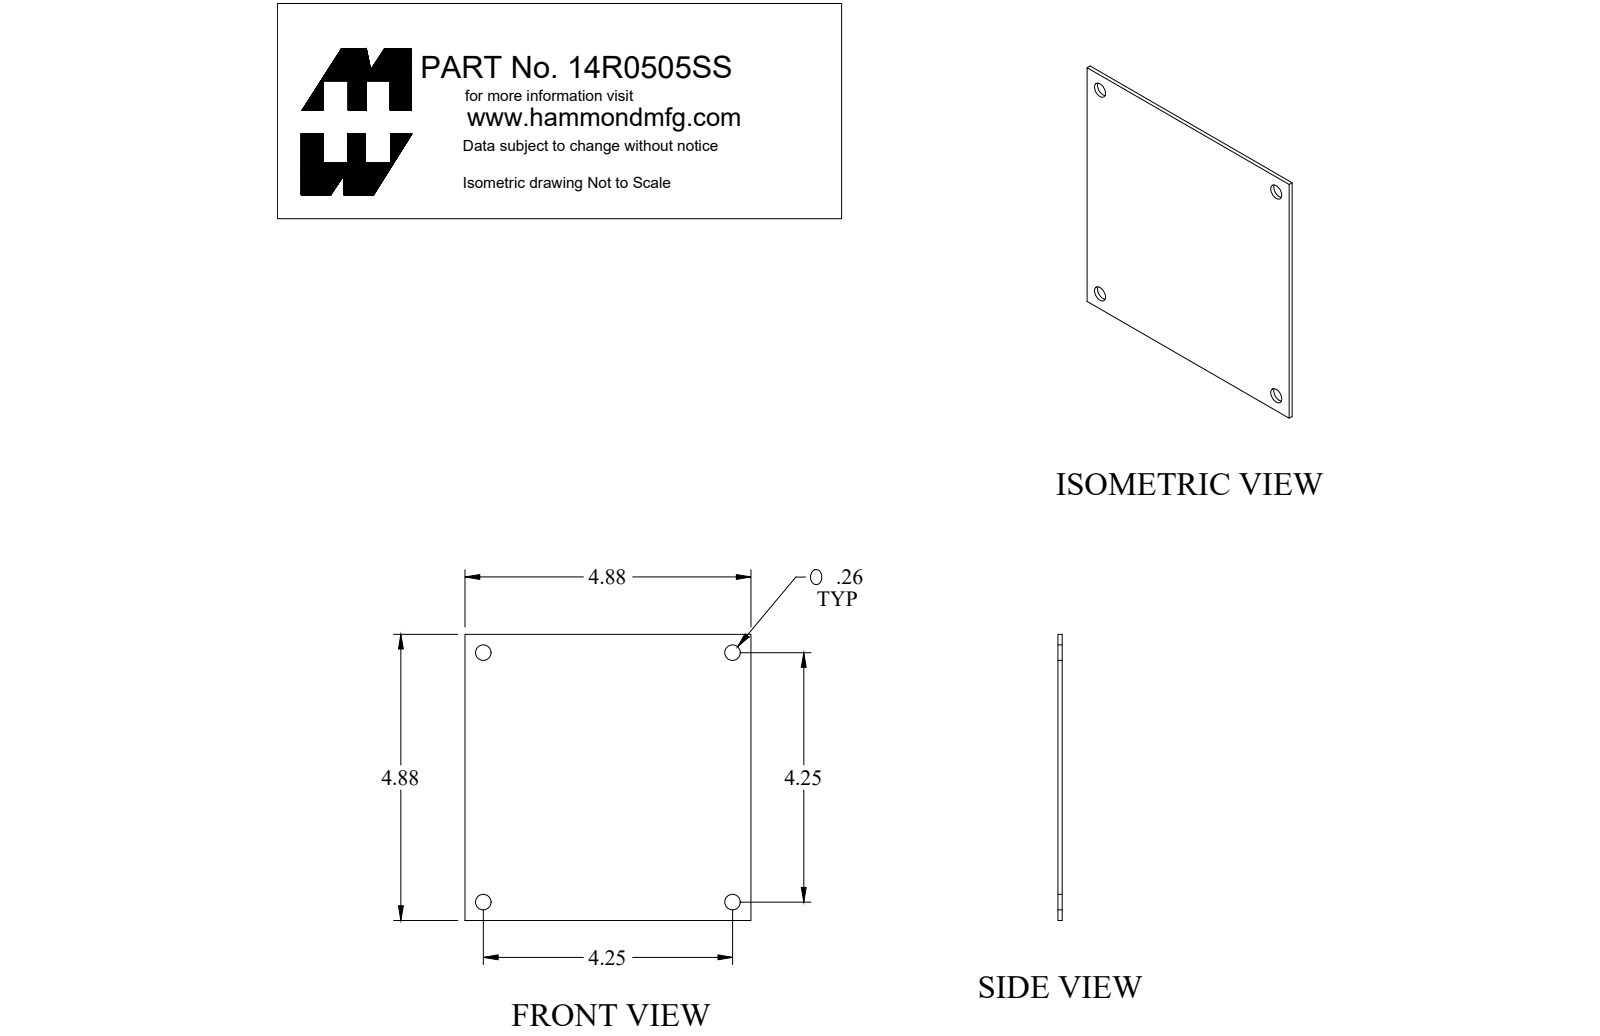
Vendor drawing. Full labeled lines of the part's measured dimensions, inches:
Part name (STEP PRODUCT): 14R0505SS
STEP written by: SolidWorks 2018 (AUTOMOTIVE_DESIGN)
Units: inches
Bodies: 1 solid, 10 faces (6 planar, 4 cylindrical, 0 other)
Overall size (bounding box): 4.875 × 4.875 × 0.072
Volume: 1.695 in³ · Surface area: 48.73 in²
Round holes (diameter × count): ⌀0.265 ×4
Main face-to-face distances: 0.072, 4.875
Hole centre spacings: 4.25, 4.25, 6.01
